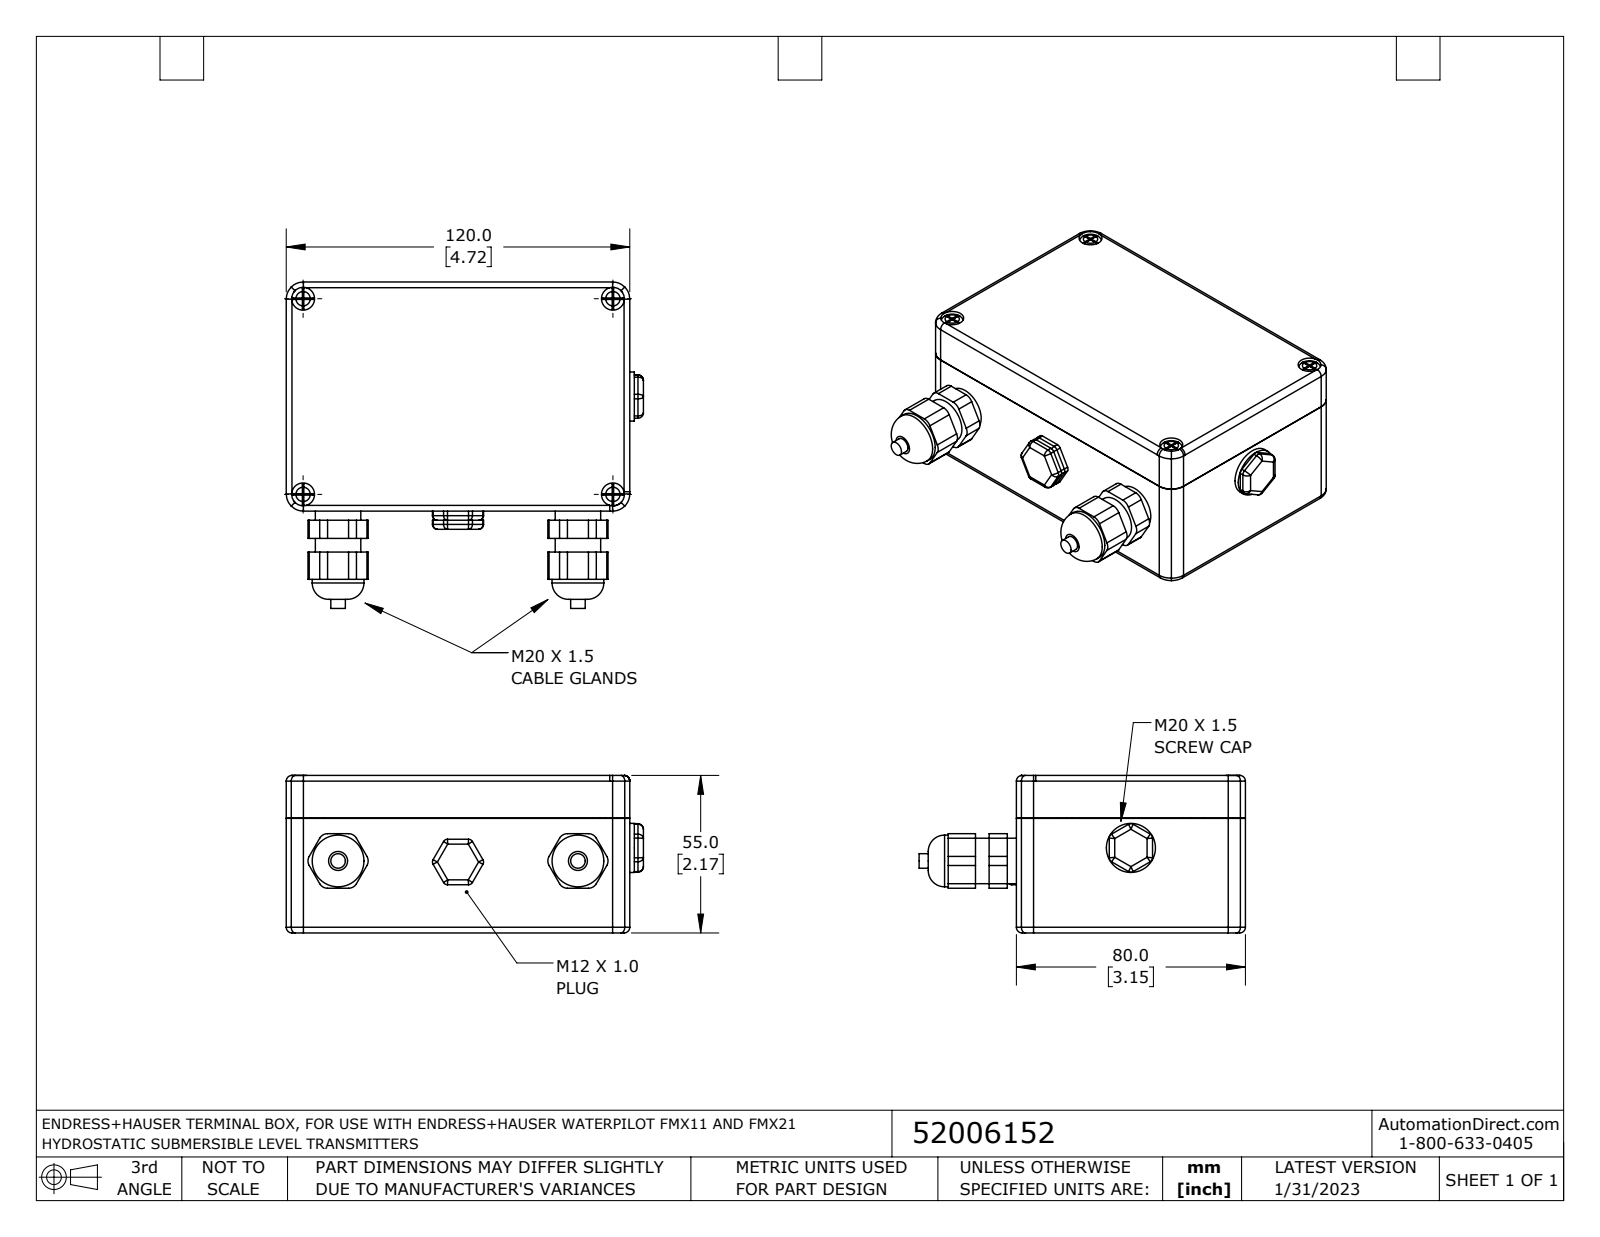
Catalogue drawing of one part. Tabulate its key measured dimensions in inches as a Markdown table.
| quantity | value |
| --- | --- |
| part name | 52006152 |
| STEP written by | SolidWorks 2021 (AUTOMOTIVE_DESIGN) |
| units | inches |
| bodies | 7 solids, 563 faces (254 planar, 109 cylindrical, 200 other) |
| overall size | 4.911 × 4.487 × 2.165 |
| volume | 8.993 in³ |
| surface area | 145.1 in² |
| round holes (diameter × count) | 0.197 × 4, 0.315 × 4 |
| round bosses / shafts (diameter × count) | 0.711 × 2, 0.625 × 2, 0.2 × 2, 0.675 × 1 |
| partial cylindrical surfaces (radius × count) | 0.062 × 16, 0.125 × 12, 0.079 × 8, 0.075 × 6, 0.063 × 4, 0.067 × 3, 0.068 × 3 |
| main face-to-face distances | 2.165, 1.972, 0.193, 1.894, 0.079, 2.087, 0.118, 3.031, 3.149, 0.059 |
| hole center spacings | 2.689, 4.26, 5.037 |
